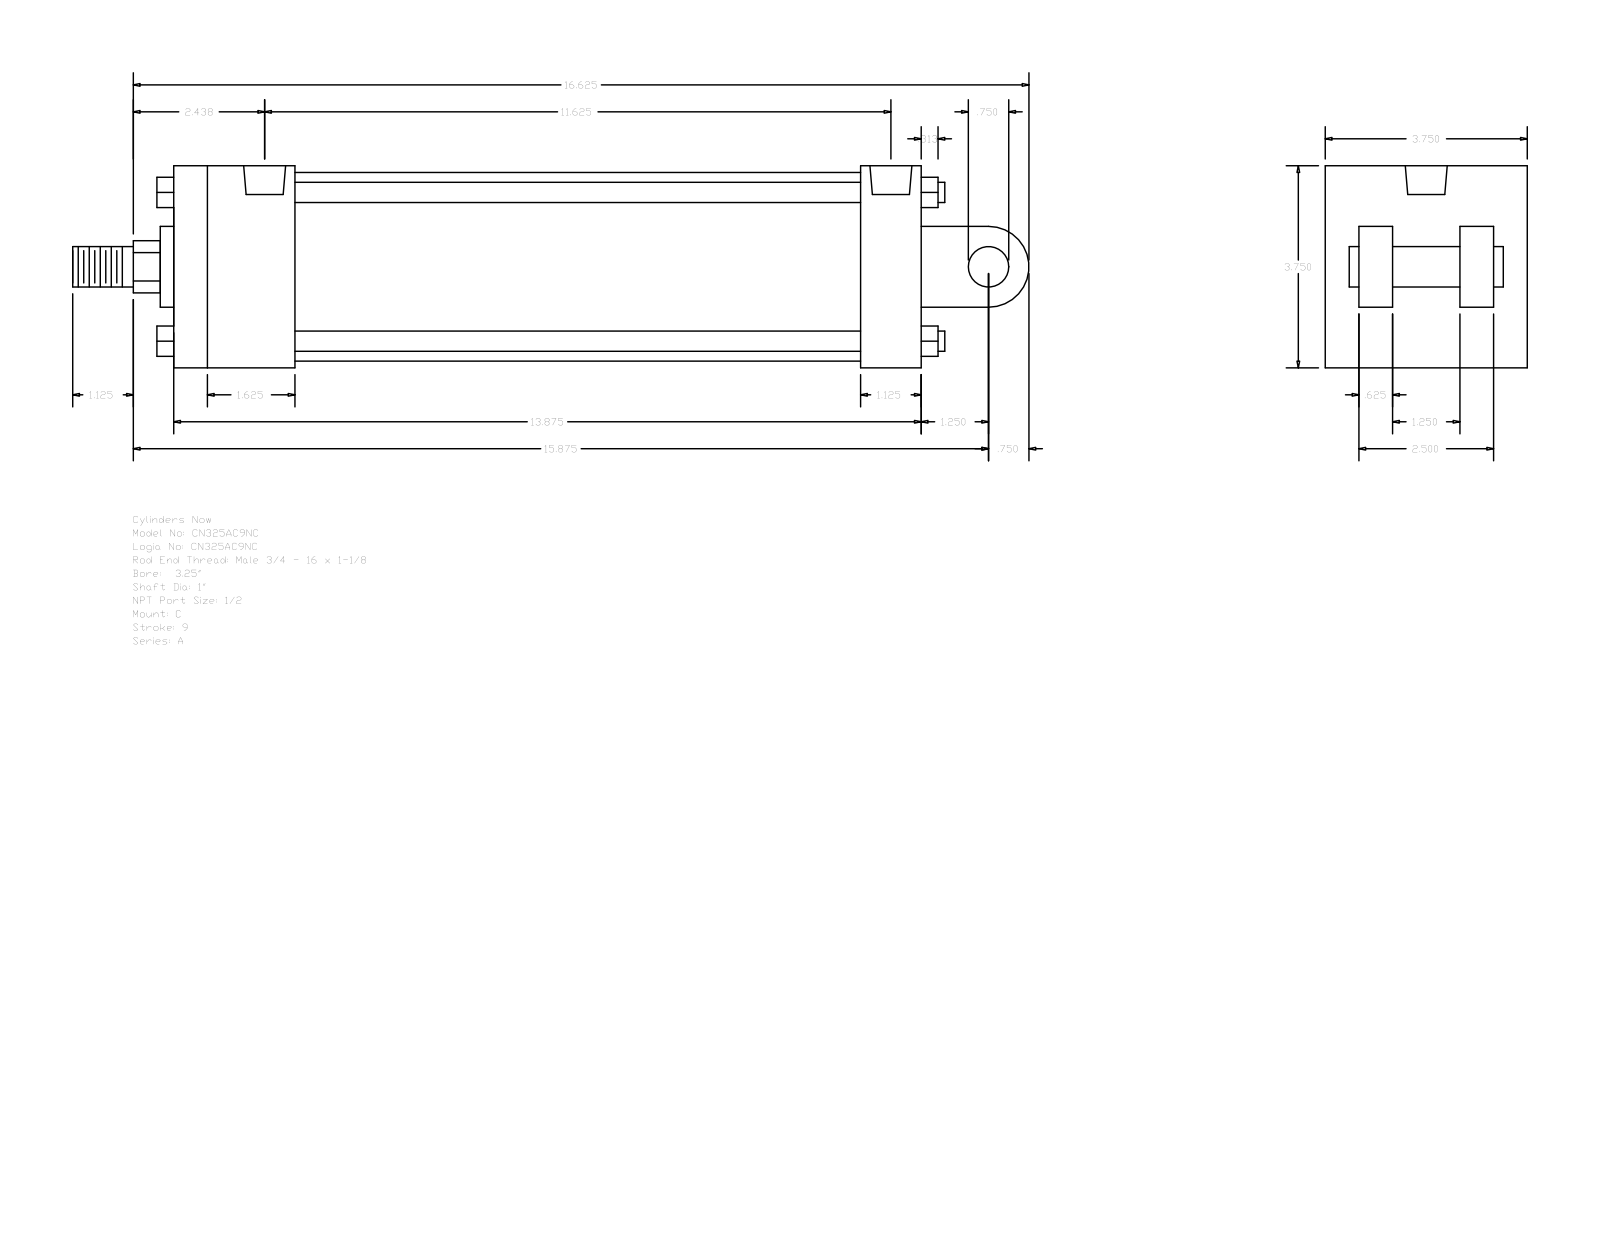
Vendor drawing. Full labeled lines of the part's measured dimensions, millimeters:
Part name (STEP PRODUCT): A_C__0325_1
STEP written by: GSSL Pune (CONFIG_CONTROL_DESIGN)
Units: millimetres
Bodies: 0 solids, 135 faces (102 planar, 33 cylindrical, 0 other)
Overall size (bounding box): 450.85 × 95.25 × 95.25
Round holes (diameter × count): ⌀8.73 ×4, ⌀19.77 ×2
Round bosses / shafts (diameter × count): ⌀9.53 ×4, ⌀19.05 ×2, ⌀88.9 ×1, ⌀38.1 ×1, ⌀25.4 ×1
Partial cylindrical surfaces — rounded edges, fillets, slot ends (radius × count): R12.29 ×1, R19.05 ×1
Main face-to-face distances: 95.24, 352.43, 15.87, 63.5, 79.37, 31.74, 47.63, 66.67, 323.85, 28.58
Hole centre spacings: 3.18, 288.92, 292.1, 295.28
